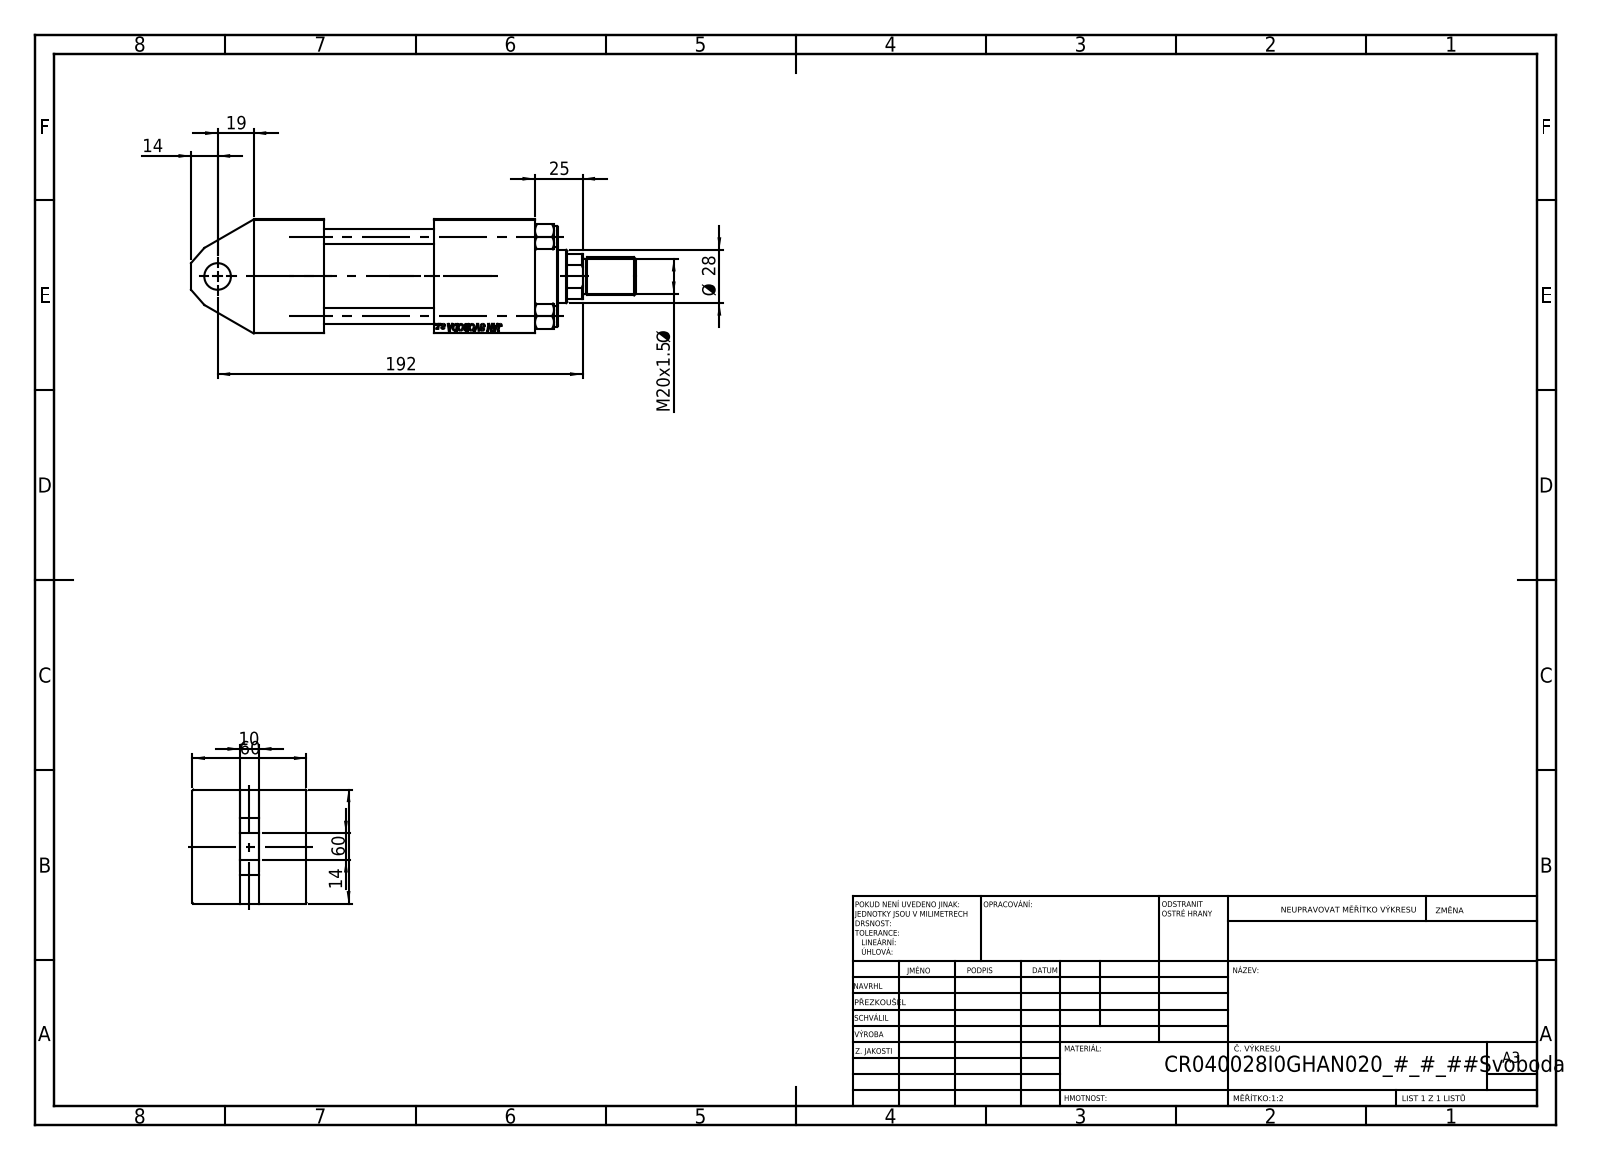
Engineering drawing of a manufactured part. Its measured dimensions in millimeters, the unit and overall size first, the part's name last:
Units: millimetres
Overall size (bounding box): 234 × 60 × 60
Round holes (diameter × count): ⌀8 ×4, ⌀7 ×2, ⌀16.66 ×2, ⌀24 ×2, ⌀14 ×1, ⌀18.5 ×1, ⌀28 ×1, ⌀31 ×1, ⌀40 ×1, ⌀45 ×1
Round bosses / shafts (diameter × count): ⌀11 ×4, ⌀46 ×1, ⌀42 ×1, ⌀20 ×1, ⌀18 ×1
Partial cylindrical surfaces — rounded edges, fillets, slot ends (radius × count): R13.5 ×1
Main face-to-face distances: 60, 37, 25, 53, 35, 58, 95, 148, 111, 119.3
Hole centre spacings: 29.49, 41.7, 58.97, 37.5, 92.5, 130
Volume: 448 508 mm³ · Surface area: 118 116 mm²
Bodies: 12 solids, 1093 faces (506 planar, 85 cylindrical, 502 other)
Part name (STEP PRODUCT): V215_VC_A; V215CR_VCP_I; NUT_M5_I; ROD_END_AH (+2 more)
STEP written by: SolidWorks 2019 (CONFIG_CONTROL_DESIGN)
